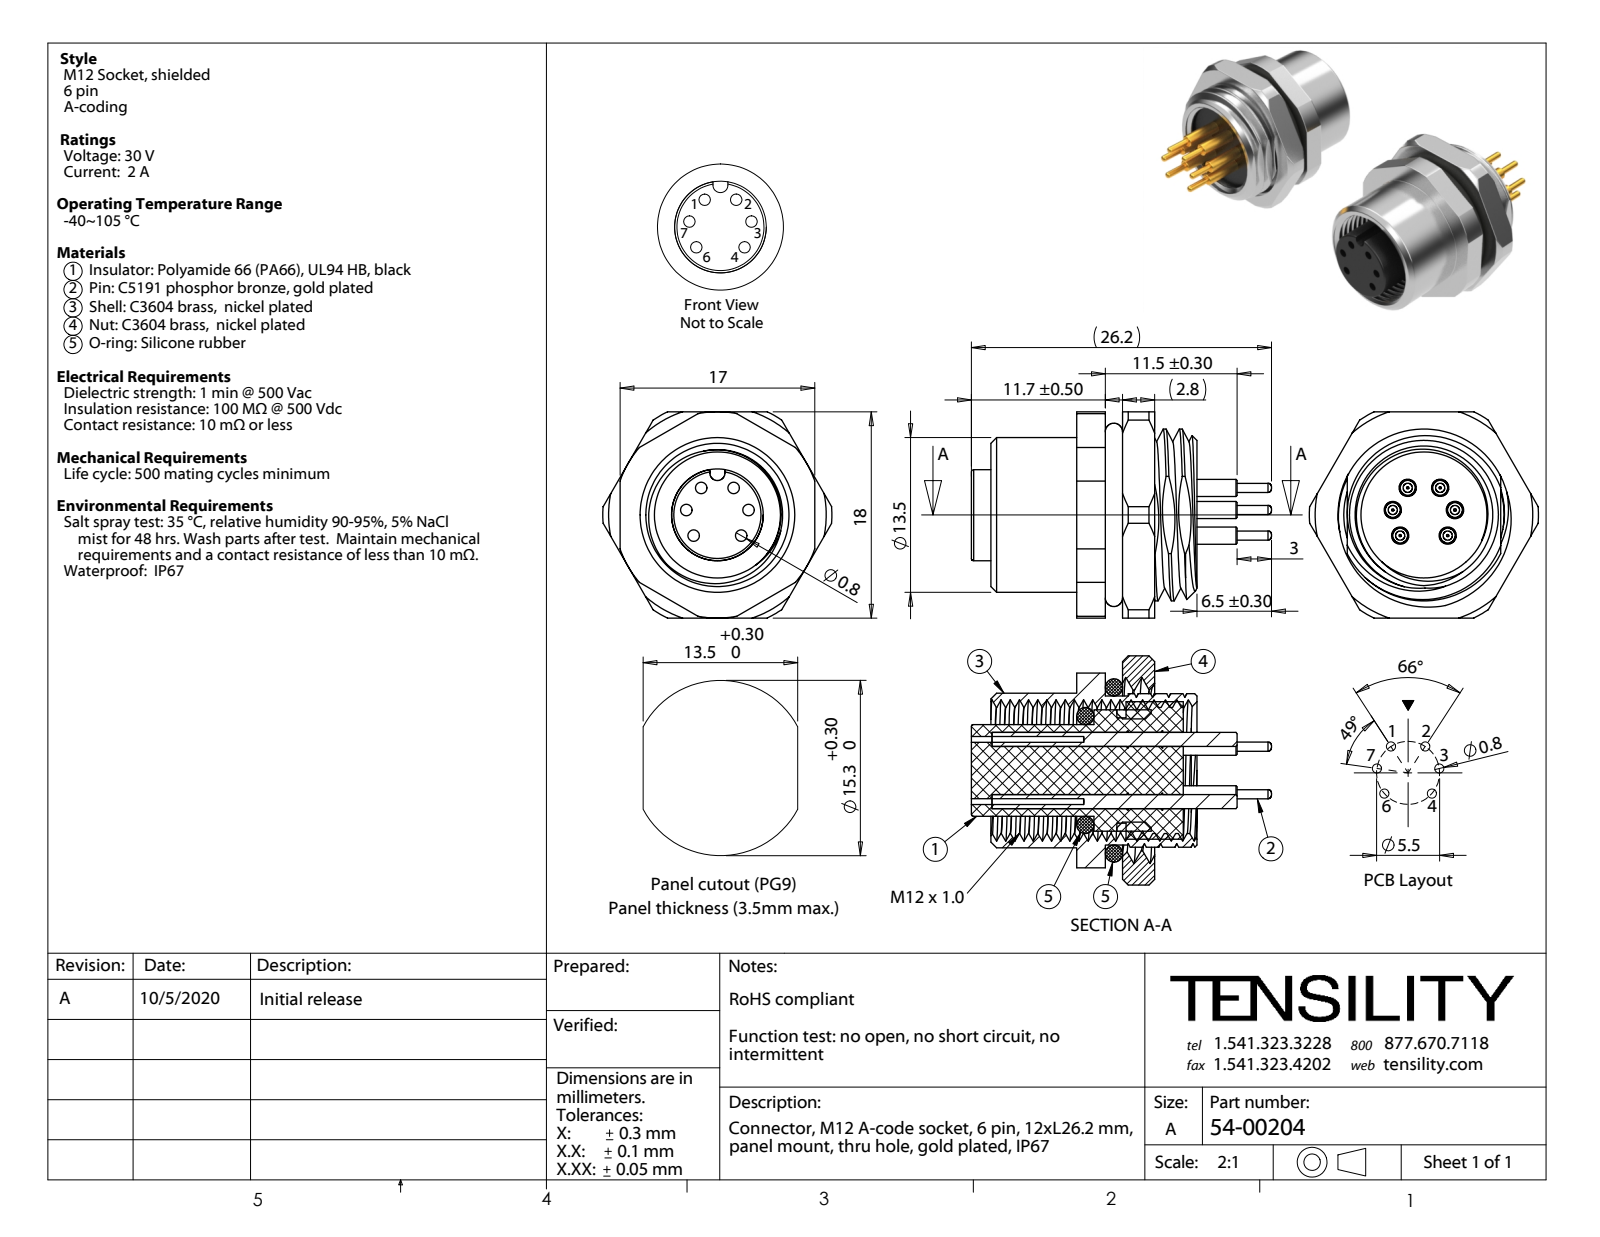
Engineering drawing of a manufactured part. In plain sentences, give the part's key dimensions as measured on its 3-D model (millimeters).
The part is named "54-00204; 54-00204-06; 54-00204-05; 54-00204-04 (+3 more)". Its 3-D file was written by "SolidWorks 2021 (CONFIG_CONTROL_DESIGN)". It is 11 solids with 399 faces: 119 planar, 167 cylindrical and 113 other. Overall it measures 26.2 by 20 by 18 millimeters. Its volume is 2 751 cubic millimeters and its surface area 5 860 square millimeters. Round holes: 6 of diameter 1, 1 of diameter 9, 1 of diameter 11, 1 of diameter 14. Round bosses or shafts: 6 of diameter 1.5, 6 of diameter 0.8, 1 of diameter 13.5, 1 of diameter 13, 1 of diameter 12, 1 of diameter 10.6, 1 of diameter 9.2, 1 of diameter 8. Partial cylindrical surfaces (rounded edges, fillets, slot ends): 1 of radius 0.65, 1 of radius 7.5, 1 of radius 9, 1 of radius 10. The main face-to-face distances are 2.5, 6.8, 2.8, 4.3, 5.3, 1.5, 4, 1, 9.3, 1.8. The hole center spacings are 2.75, 5.44, 2.32, 2.33, 4.21, 4.57, 5.29, 2.84.
